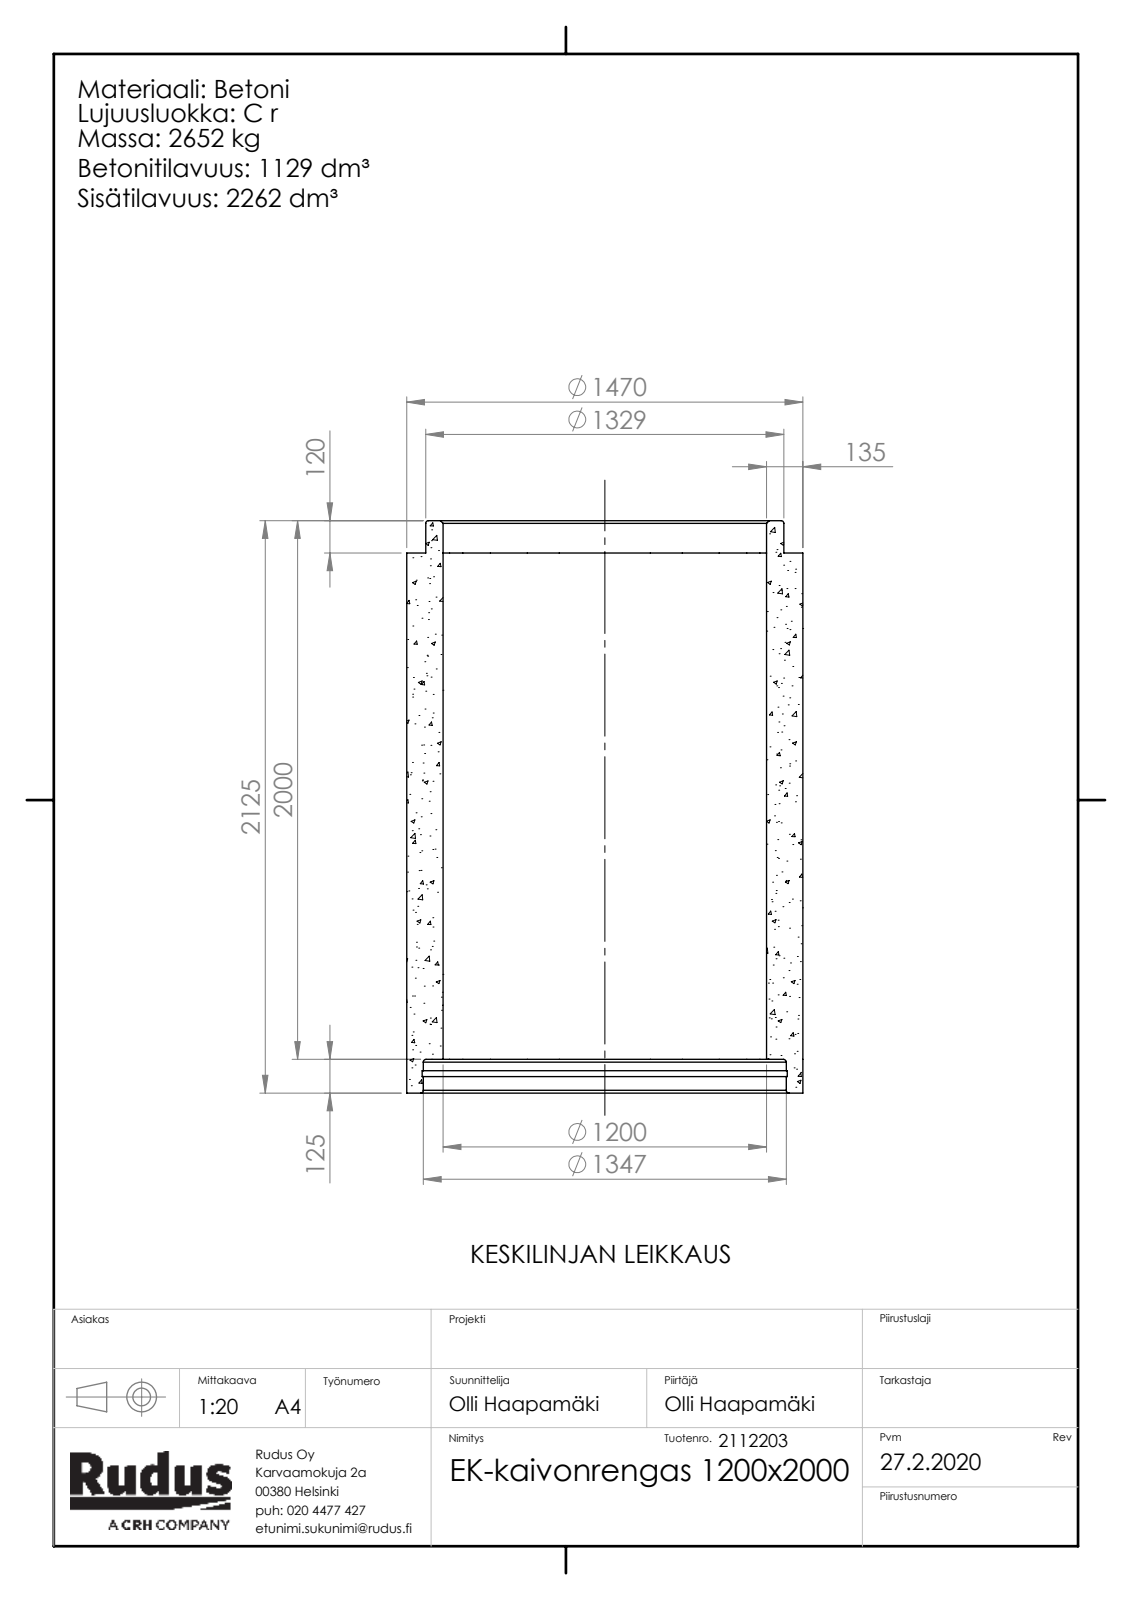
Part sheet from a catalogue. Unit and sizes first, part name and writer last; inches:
Units: inches
Overall size (bounding box): 83.661 × 57.874 × 57.874
Round holes (diameter × count): ⌀47.244 ×1, ⌀53.016 ×1, ⌀53.331 ×1
Round bosses / shafts (diameter × count): ⌀57.874 ×1, ⌀52.307 ×1
Main face-to-face distances: 74.016, 4.921, 78.937, 83.661, 78.74, 4.724, 2.402, 3.268, 0.866, 2.52
Volume: 68 900 in³ · Surface area: 29 330 in²
Bodies: 1 solid, 107 faces (7 planar, 12 cylindrical, 88 other)
Part name (STEP PRODUCT): EK-osa-kaivorunko_EK-kaivonrengas; Rudus 2112203 EK-kaivonrengas 1200x2000
STEP written by: SolidWorks 2019 (CONFIG_CONTROL_DESIGN)
